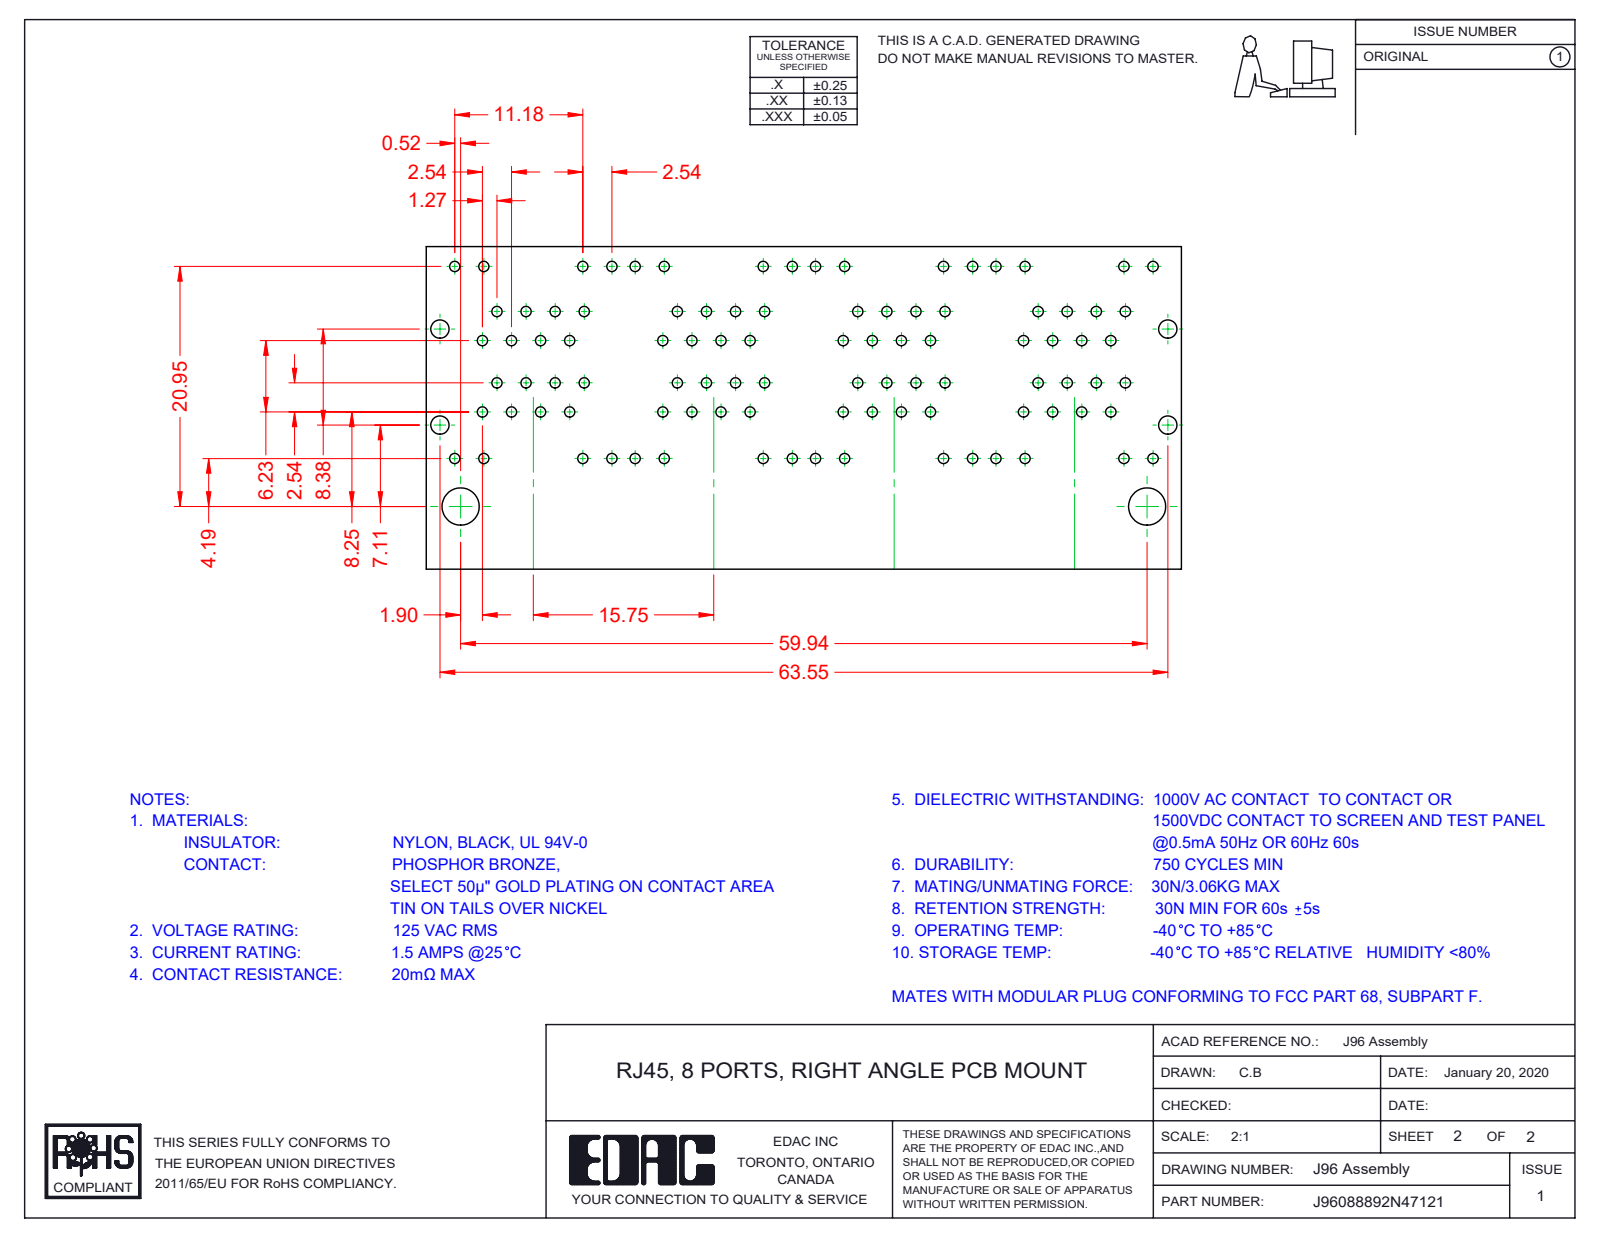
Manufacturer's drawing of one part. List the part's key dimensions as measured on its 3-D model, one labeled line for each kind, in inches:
Part name (STEP PRODUCT): 96 Back Plate_8 Ports; 96 LED RH Lower_7-Green-Orange; 96 LED LH Upper_4-Orange; 96 Insulator_8 Ports (+8 more)
STEP written by: SolidWorks 2016 (CONFIG_CONTROL_DESIGN)
Units: inches
Bodies: 96 solids, 7658 faces (6069 planar, 1323 cylindrical, 266 other)
Overall size (bounding box): 2.522 × 1.165 × 1.129
Volume: 1.474 in³ · Surface area: 98.67 in²
Round holes (diameter × count): ⌀0.067 ×3
Round bosses / shafts (diameter × count): ⌀0.066 ×3
Partial cylindrical surfaces — rounded edges, fillets, slot ends (radius × count): R0.01 ×124, R0.014 ×73, R0.039 ×72, R0.02 ×49, R0.036 ×32, R0.008 ×21, R0.028 ×11, R0.009 ×8
Main face-to-face distances: 0.62, 0.014, 0.392, 0.046, 0.063, 0.021, 0.393, 0.401, 0.499, 0.133
Hole centre spacings: 0.62, 1.24
